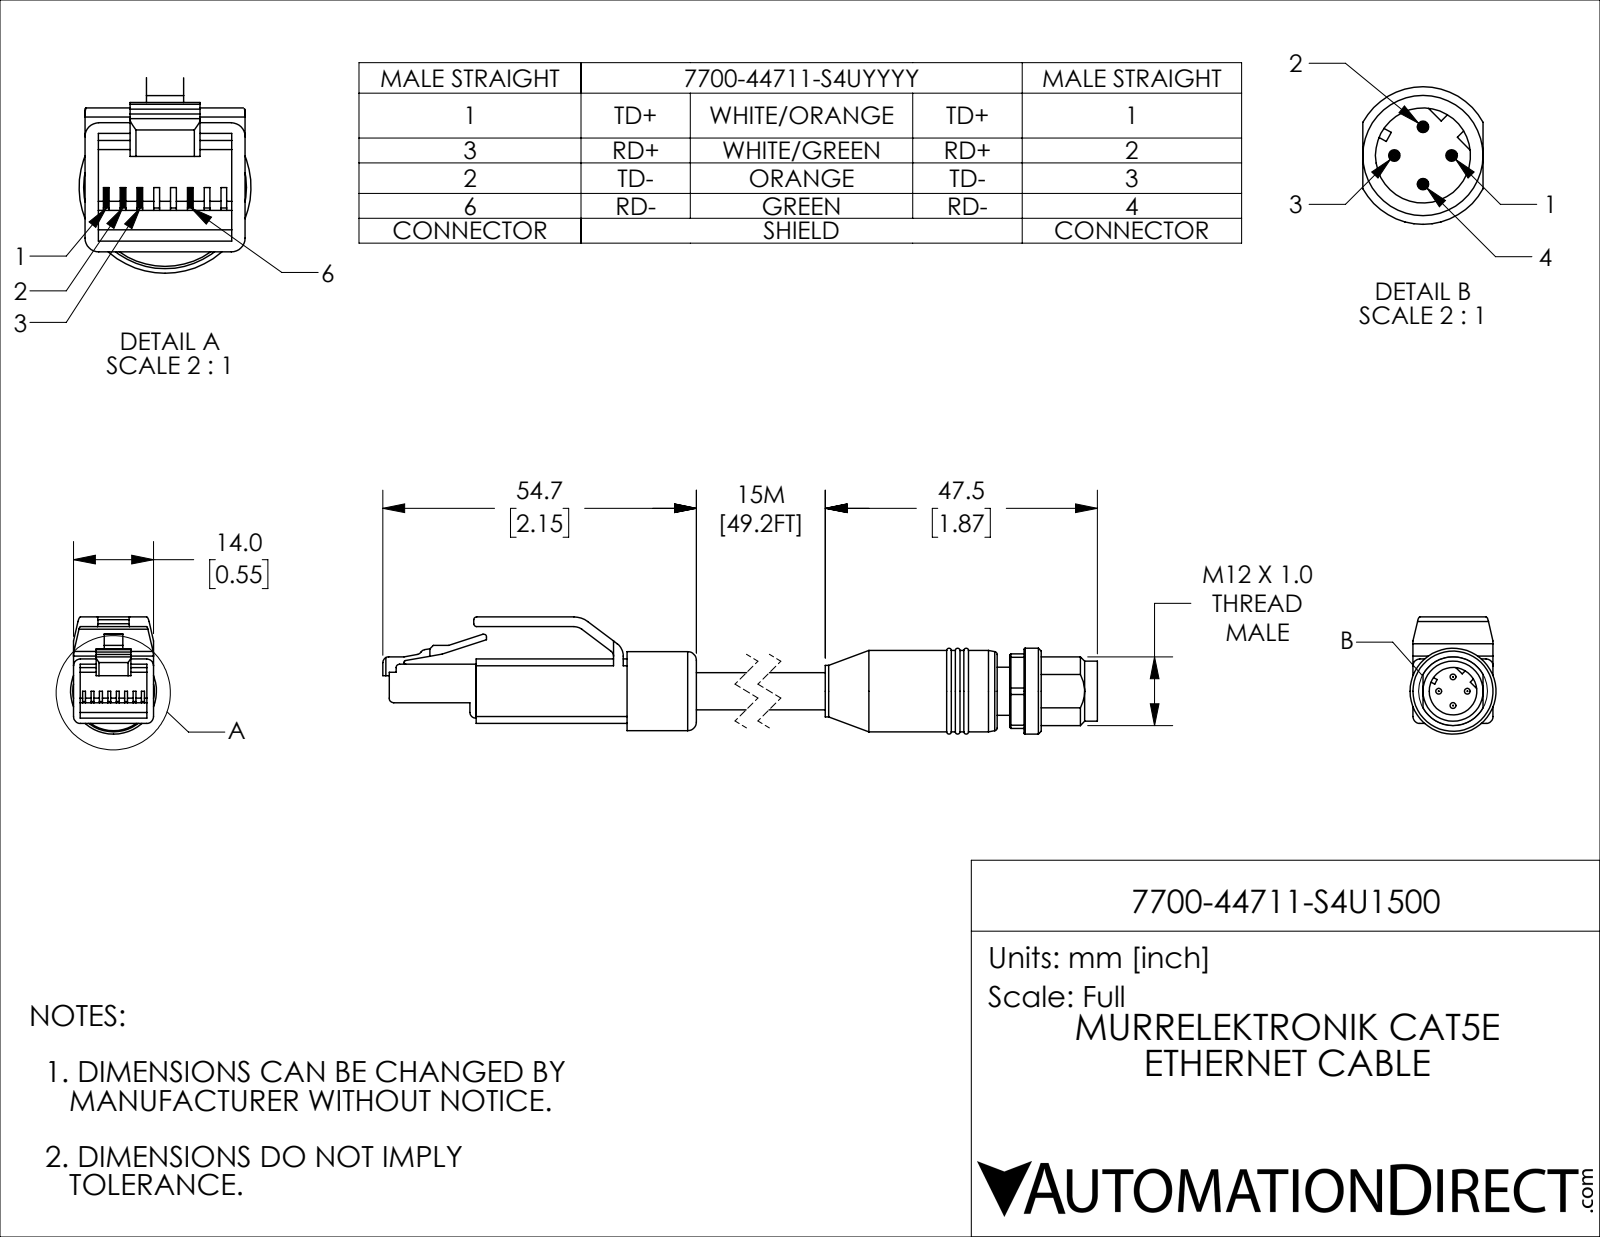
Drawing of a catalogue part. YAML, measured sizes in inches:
part_name: "7700-44711-S4U1500_2; 7700-44711-S4U1500; 7700-44711-S4U1500_1"
step_written_by: "SolidWorks 2021 (CONFIG_CONTROL_DESIGN)"
units: inches
bodies: {solids: 3, faces: 266, planar: 151, cylindrical: 73, other: 42}
overall_size: [5.854, 0.806, 0.591]
volume: 0.912
surface_area: 11.41
round_holes:
  - {diameter: 0.327, count: 1}
round_bosses_or_shafts:
  - {diameter: 0.039, count: 4}
  - {diameter: 0.591, count: 1}
  - {diameter: 0.559, count: 1}
  - {diameter: 0.543, count: 1}
  - {diameter: 0.413, count: 1}
  - {diameter: 0.354, count: 1}
  - {diameter: 0.331, count: 1}
  - {diameter: 0.256, count: 1}
partial_cylinders:
  - {radius: 0.047, count: 6}
  - {radius: 0.02, count: 5}
  - {radius: 0.039, count: 5}
  - {radius: 0.012, count: 2}
  - {radius: 0.024, count: 1}
  - {radius: 0.031, count: 1}
  - {radius: 0.091, count: 1}
  - {radius: 0.106, count: 1}
face_to_face_distances: [0.444, 0.55, 0.067, 0.046, 0.504, 0.037, 0.407, 0.222, 0.665, 0.732]
